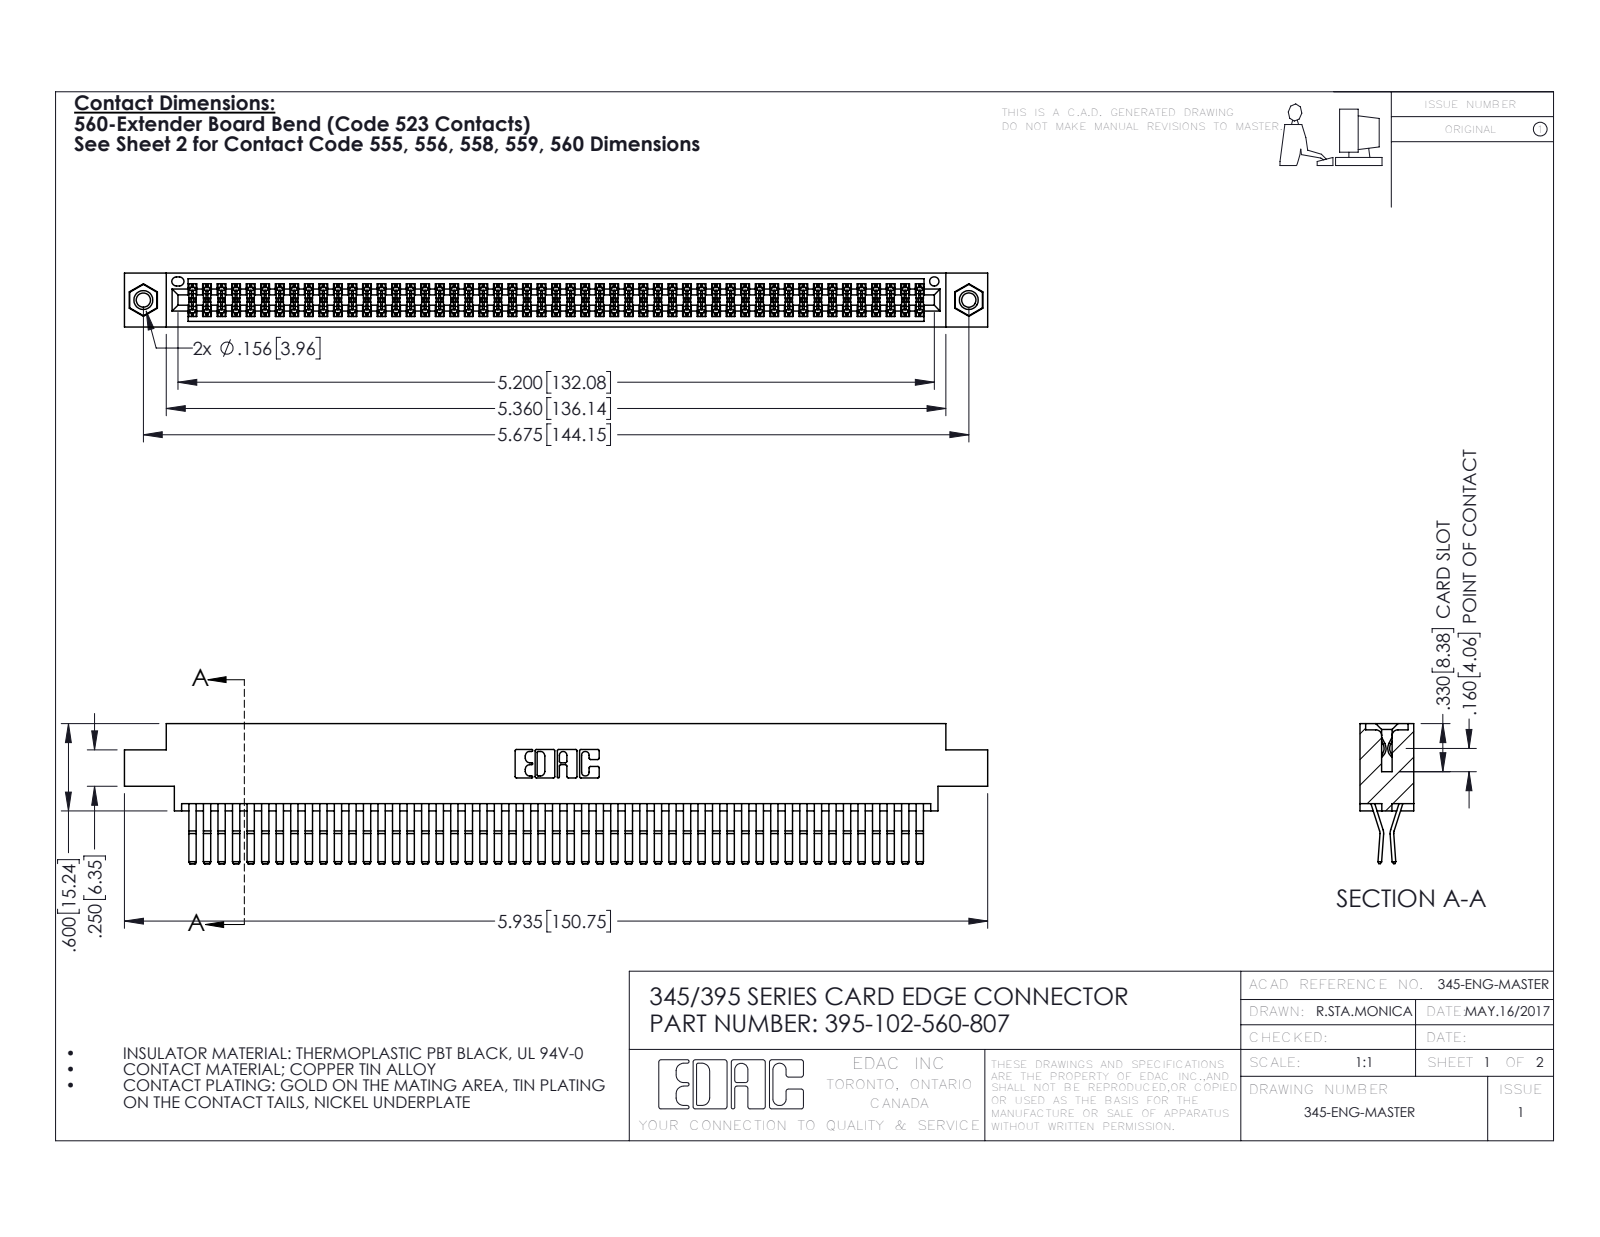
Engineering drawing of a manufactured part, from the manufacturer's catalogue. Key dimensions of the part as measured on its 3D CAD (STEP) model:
Part name (STEP PRODUCT): 345-250-001_345-250-005-103; 395-102-560-807; 345 Part_0.170 Offset - 0.156 Dia-TI; 345-292-001_560 Tail
STEP written by: SolidWorks 2016 (CONFIG_CONTROL_DESIGN)
Units: inches
Bodies: 105 solids, 5494 faces (3482 planar, 1996 cylindrical, 16 other)
Overall size (bounding box): 5.935 × 0.962 × 0.37
Volume: 0.932 in³ · Surface area: 38.19 in²
Round holes (diameter × count): ⌀0.098 ×2, ⌀0.125 ×2, ⌀0.156 ×2, ⌀0.064 ×1
Round bosses / shafts (diameter × count): ⌀0.155 ×2
Partial cylindrical surfaces — rounded edges, fillets, slot ends (radius × count): R0.006 ×154, R0.01 ×22, R0.007 ×6, R0.031 ×6, R0.026 ×3, R0.01 ×2, R0.014 ×2, R0.019 ×2
Main face-to-face distances: 0.025, 0.072, 0.298, 0.37, 0.2, 0.098, 0.272, 0.225, 0.175, 0.149
Hole centre spacings: 0.27, 5.439, 5.675
